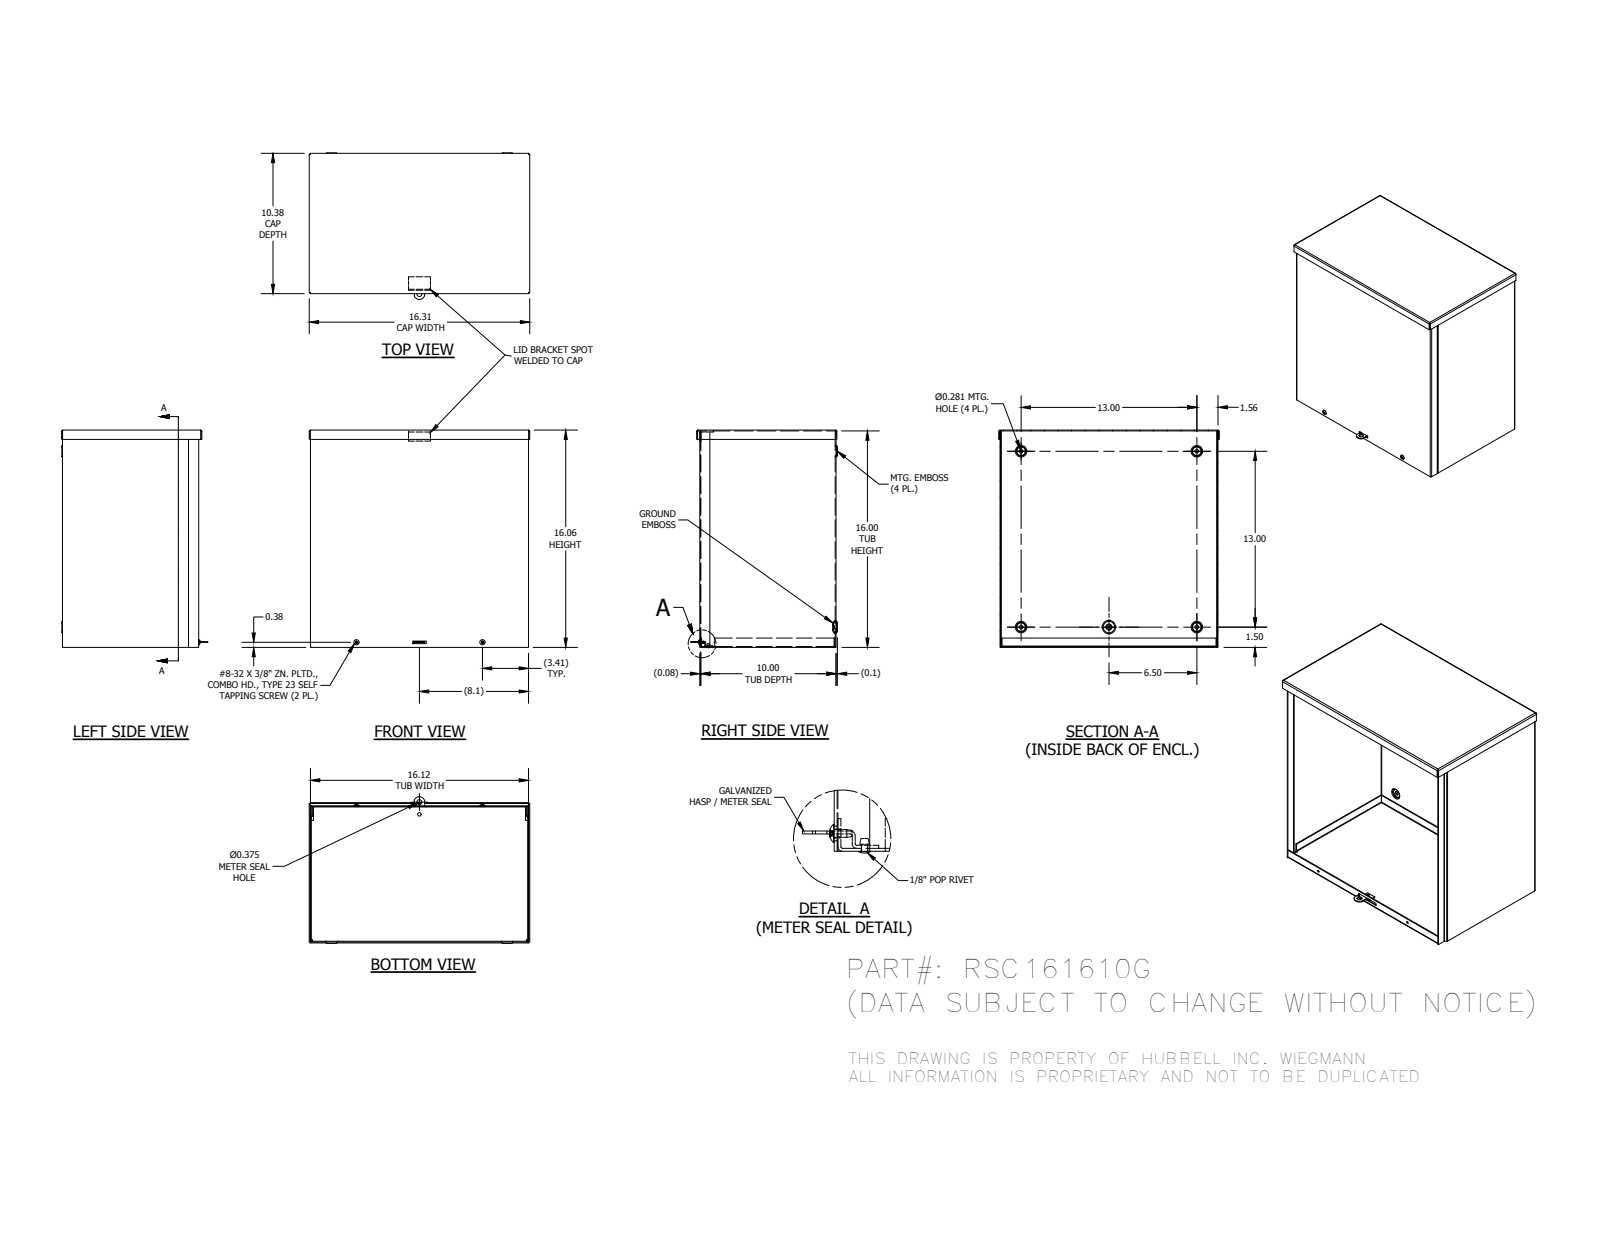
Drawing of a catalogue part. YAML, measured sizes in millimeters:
part_name: "RSC161610GBKPA; RSC1610GEWPA; RSC1616GLFA; RSC1610GCPA (+5 more)"
step_written_by: "Autodesk Inventor 2014 (AUTOMOTIVE_DESIGN)"
units: millimeters
bodies: {solids: 9, faces: 320, planar: 183, cylindrical: 61, other: 76}
overall_size: [414.31, 408.99, 275.6]
volume: 1270000
surface_area: 1625000
round_holes:
  - {diameter: 7.14, count: 4}
  - {diameter: 7.94, count: 4}
  - {diameter: 3.73, count: 2}
  - {diameter: 3.17, count: 1}
  - {diameter: 3.45, count: 1}
  - {diameter: 4.34, count: 1}
  - {diameter: 9.52, count: 1}
round_bosses_or_shafts:
  - {diameter: 9.75, count: 2}
  - {diameter: 4.17, count: 2}
  - {diameter: 6.65, count: 1}
  - {diameter: 5.93, count: 1}
  - {diameter: 3.17, count: 1}
partial_cylinders:
  - {radius: 0.79, count: 19}
  - {radius: 2.37, count: 18}
  - {radius: 2.67, count: 1}
  - {radius: 10.16, count: 1}
face_to_face_distances: [1.57, 254.4, 406.4, 407.97, 255.97, 252.83, 404.83, 409.54, 1.58, 6.41]
hole_center_spacings: [54.86, 284.81, 236.54, 121.67, 330.2, 361.82, 457.19, 165.1]
